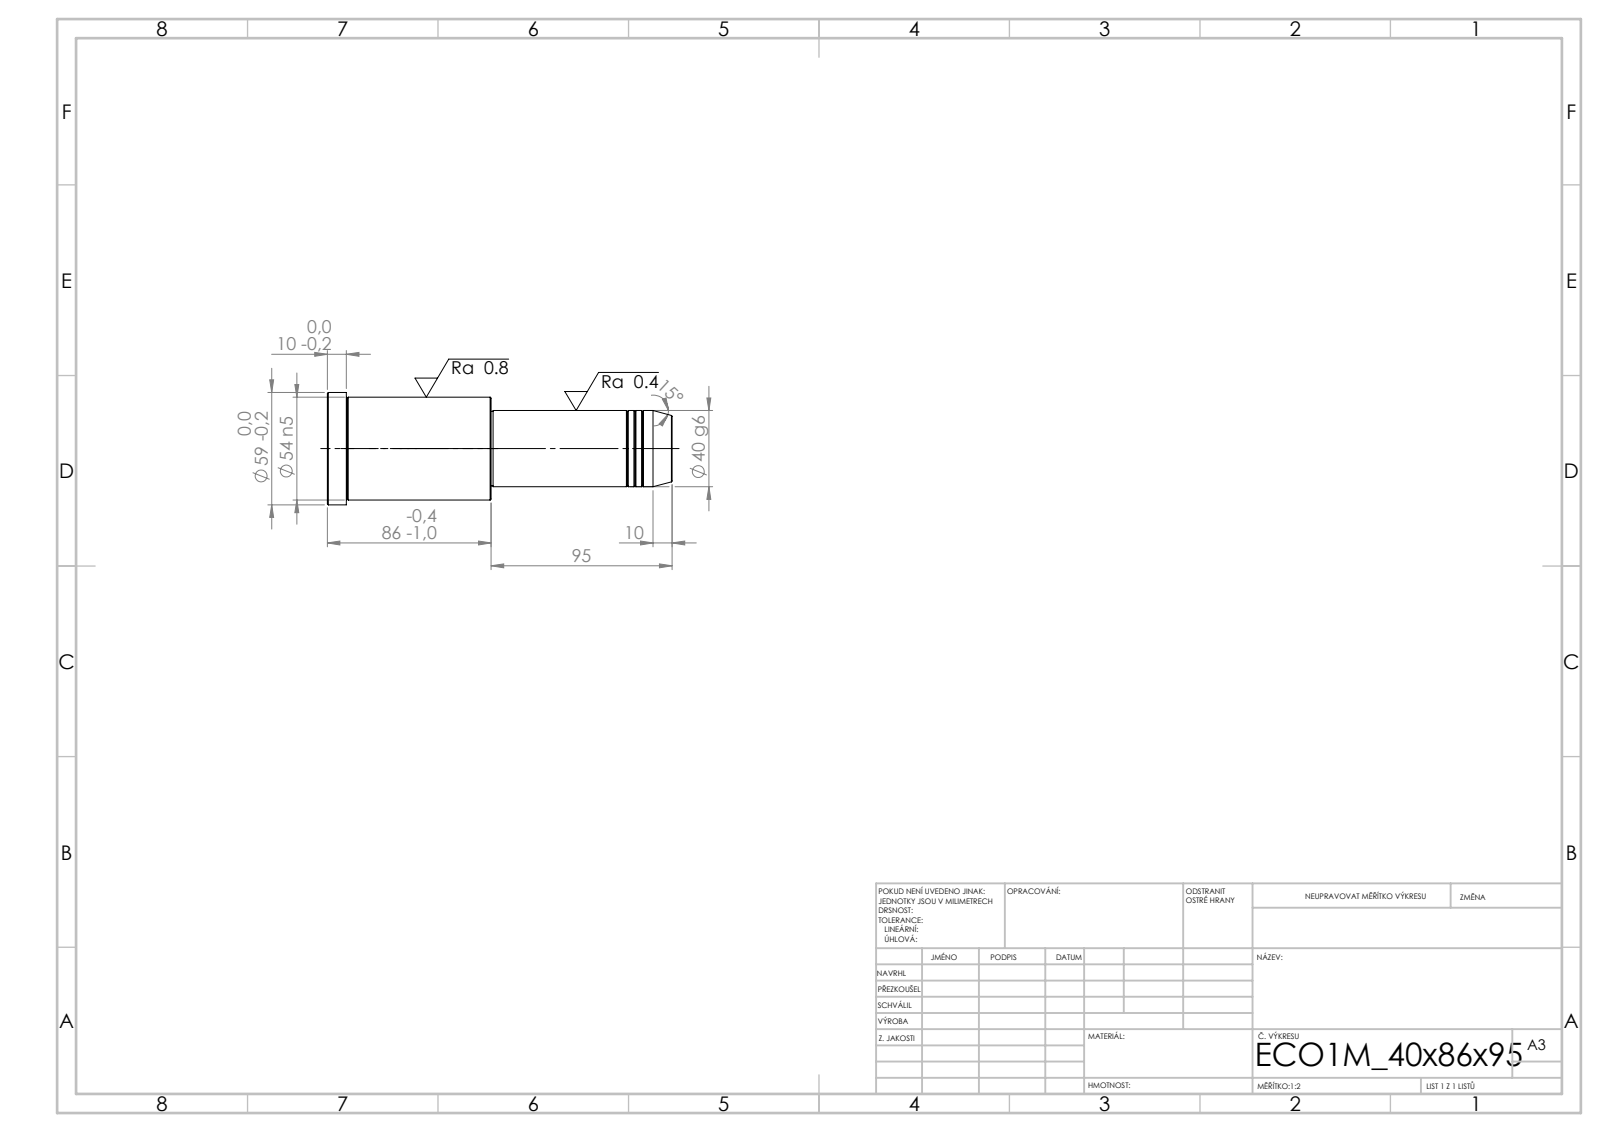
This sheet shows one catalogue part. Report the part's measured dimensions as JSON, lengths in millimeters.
{"step_written_by": "SolidWorks 2019 (CONFIG_CONTROL_DESIGN)", "units": "millimeters", "bodies": {"solids": 1, "faces": 43, "planar": 5, "cylindrical": 14, "other": 24}, "overall_size": [181, 59, 59], "volume_mm3": 318847, "surface_area_mm2": 32099, "round_bosses_or_shafts": [[59, 1], [54, 1], [40, 1], [39, 1]], "face_to_face_distances": [86, 95, 181, 171, 76, 10, 94, 1, 77, 87]}
